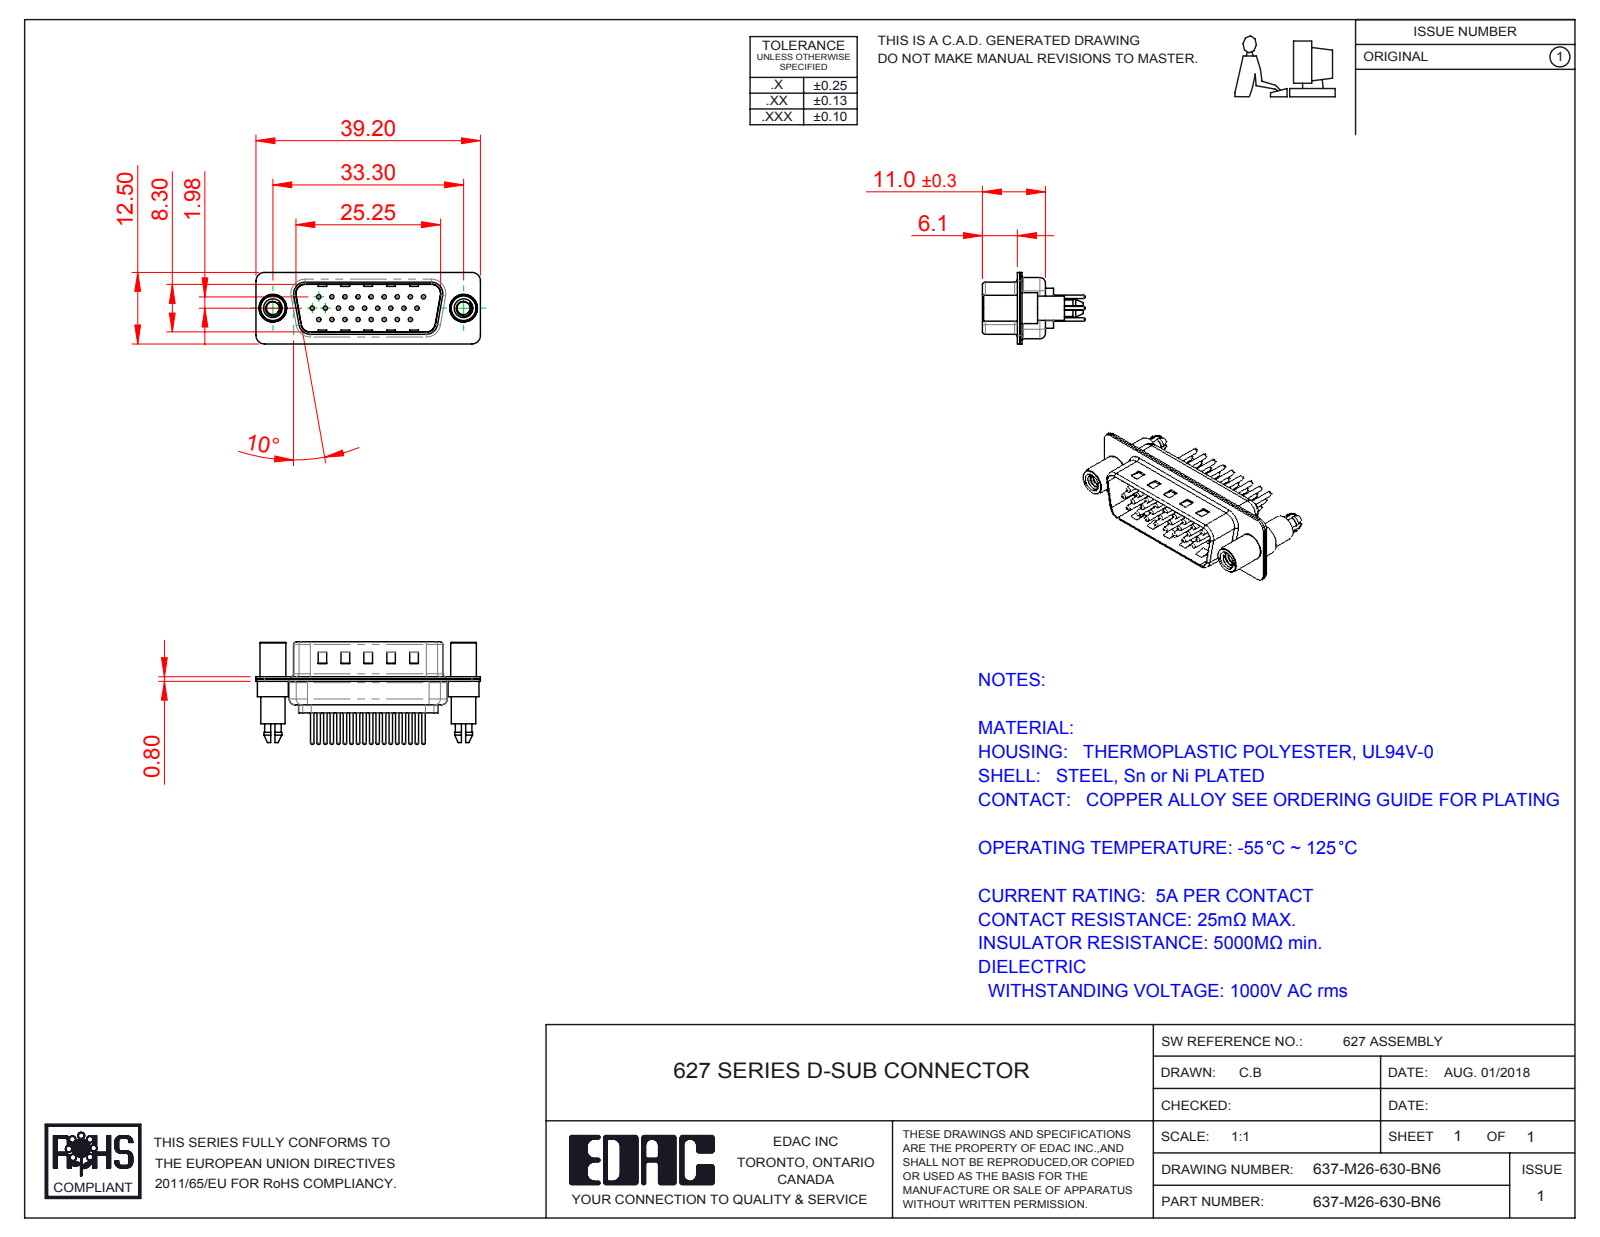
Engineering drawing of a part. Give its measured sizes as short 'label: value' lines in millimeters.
name: 637M Contact Row 1_30; 637M Housing_26 Contacts; 637-M26-630-BN6; 637M 4-40 Threaded Standoff and Boardlock (+4 more)
written by: SolidWorks 2016 (CONFIG_CONTROL_DESIGN)
unit: mm
bodies: 31 solids, 1386 faces (359 planar, 533 cylindrical, 494 other)
size: 39.2 × 17.9 × 12.5
volume: 2 246 mm³; area: 6 235 mm²
holes: 26× ⌀0.75, 26× ⌀1.6, 26× ⌀2, 2× ⌀2.26, 2× ⌀4, 2× ⌀4.8
bosses: 26× ⌀1.5, 26× ⌀0.6, 2× ⌀5.4, 2× ⌀4.9, 2× ⌀4.5, 2× ⌀4.25
rounds: 18× R1.5, 12× R2, 10× R1.6, 8× R0.5, 4× R0.25, 4× R0.6, 4× R0.65, 4× R0.9
face distances: 0.4, 0.8, 9.5, 9.1, 8.7, 9.9, 0.75, 6.3, 5.5, 0.35
hole spacings: 3.96, 2.28, 4.57, 6.05, 2.29, 8.24, 6.86, 10.48
